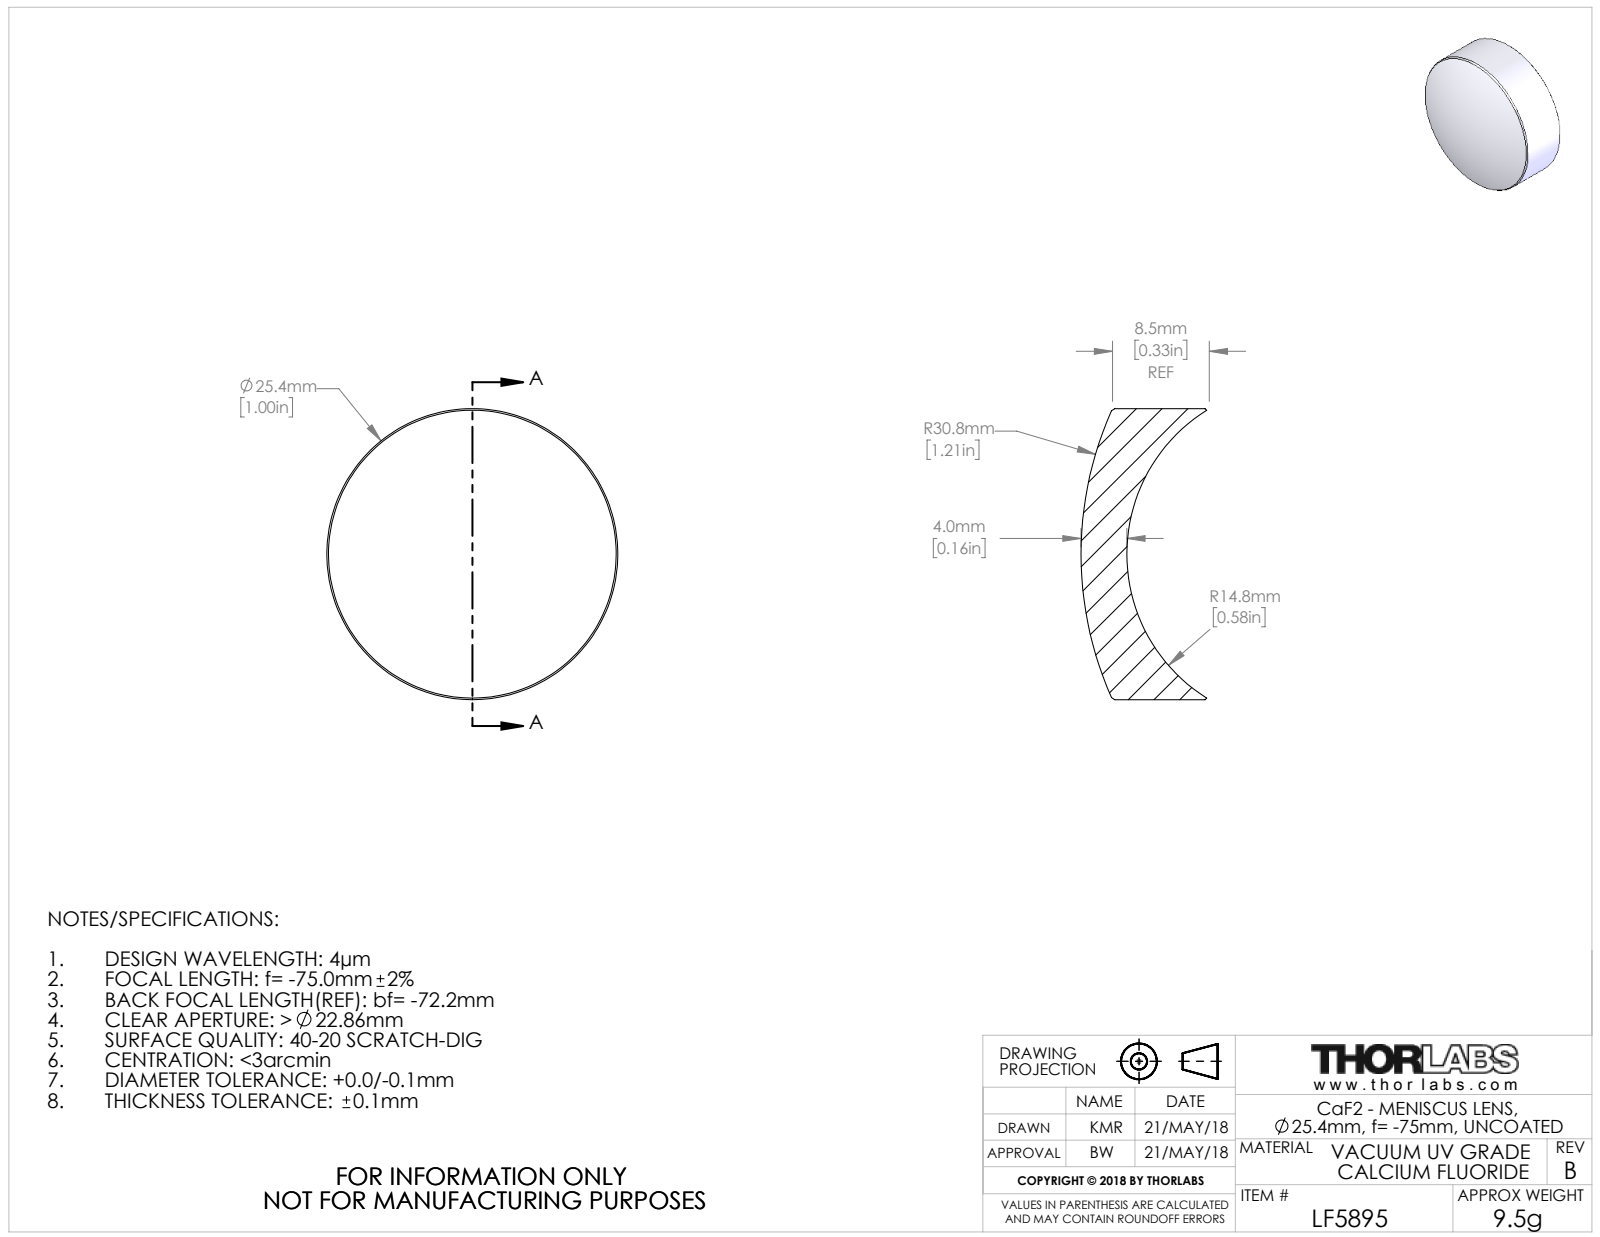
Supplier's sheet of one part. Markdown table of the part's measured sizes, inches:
| quantity | value |
| --- | --- |
| part name | 22000-E0W |
| STEP written by | SolidWorks 2016 (CONFIG_CONTROL_DESIGN) |
| units | inches |
| bodies | 1 solid, 10 faces (0 planar, 2 cylindrical, 8 other) |
| overall size | 1 × 1 × 0.432 |
| volume | 0.181 in³ |
| surface area | 2.844 in² |
| round bosses / shafts (diameter × count) | 1 × 1 |
